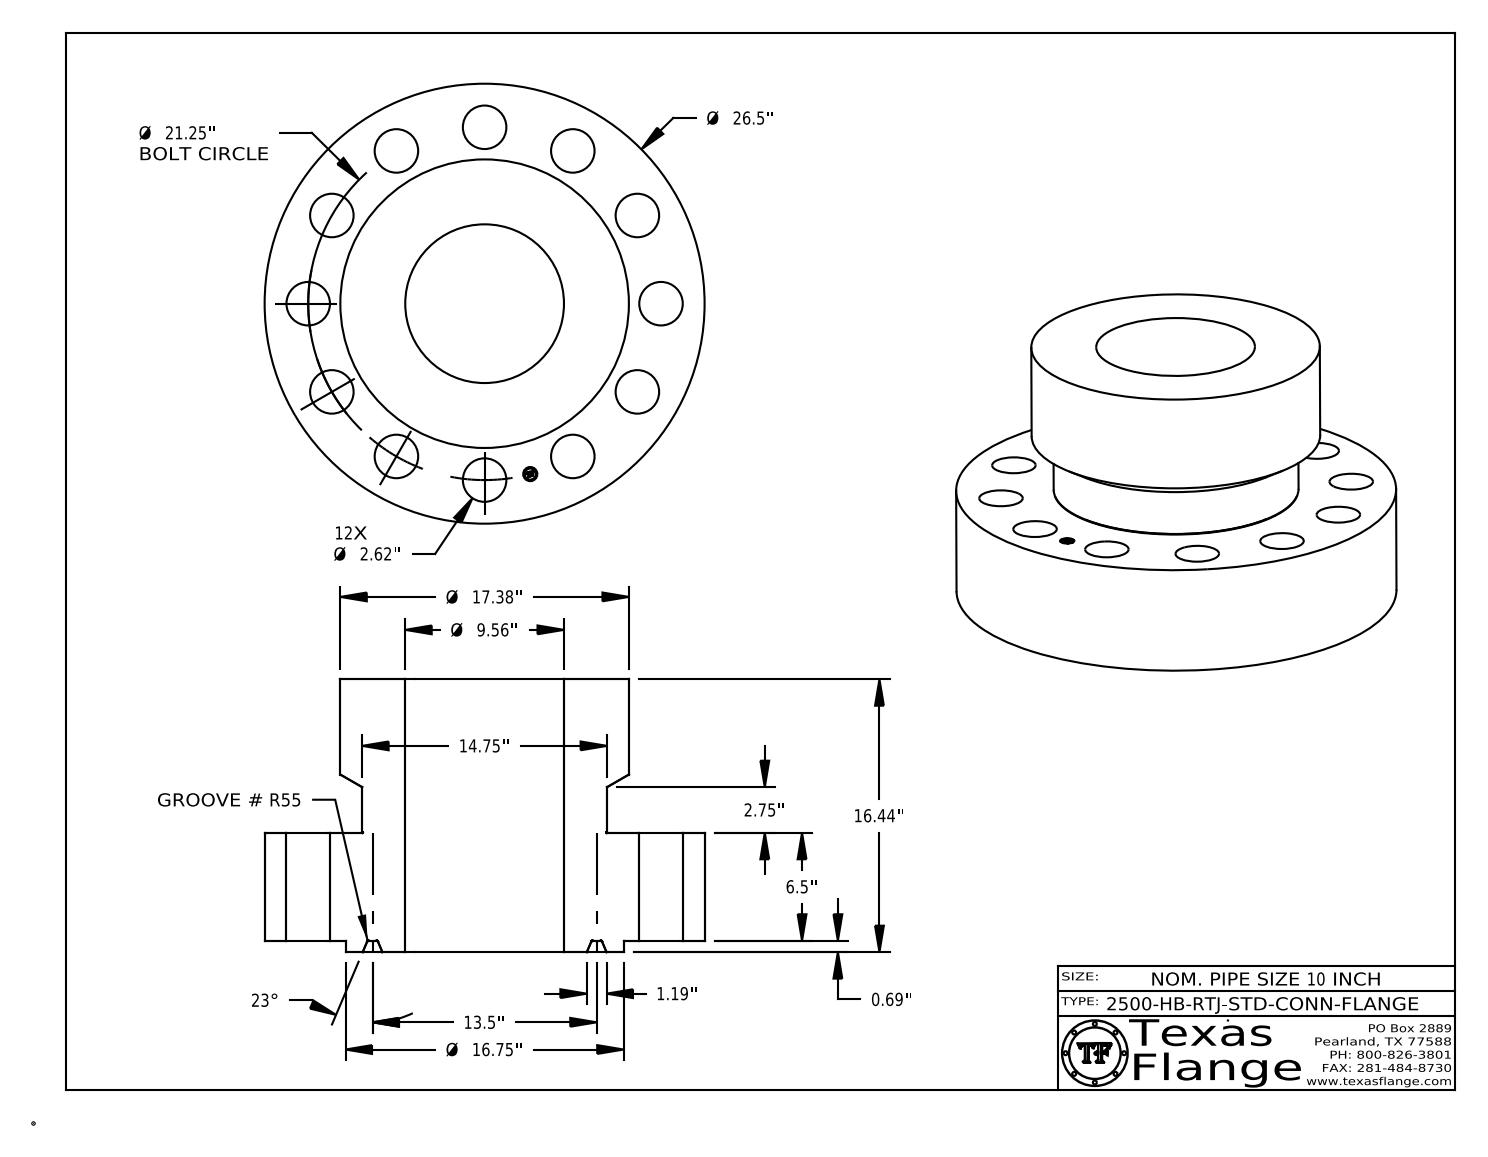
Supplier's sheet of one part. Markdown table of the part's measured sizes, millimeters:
| quantity | value |
| --- | --- |
| part name | 10-2500-HB-RTJ-STD-CONN-FLANGE |
| STEP written by | CATIA V5 STEP AP214 (AUTOMOTIVE_DESIGN) |
| units | millimeters |
| bodies | 1 solid, 439 faces (371 planar, 54 cylindrical, 14 other) |
| overall size | 673.1 × 673.1 × 417.5 |
| volume | 67 120 000 mm³ |
| surface area | 2 043 000 mm² |
| round holes (diameter × count) | 66.5 × 12, 21.6 × 1, 242.8 × 1 |
| round bosses / shafts (diameter × count) | 1.3 × 8, 673.1 × 1, 441.5 × 1, 425.5 × 1, 374.7 × 1, 17 × 1 |
| main face-to-face distances | 165.1, 400.1, 235, 17.5, 182.6, 417.5, 182.4, 165, 235.1, 6.5 |
| hole center spacings | 269.9, 139.7, 467.4, 381.7, 521.4, 381.7, 521.4, 539.8 |
